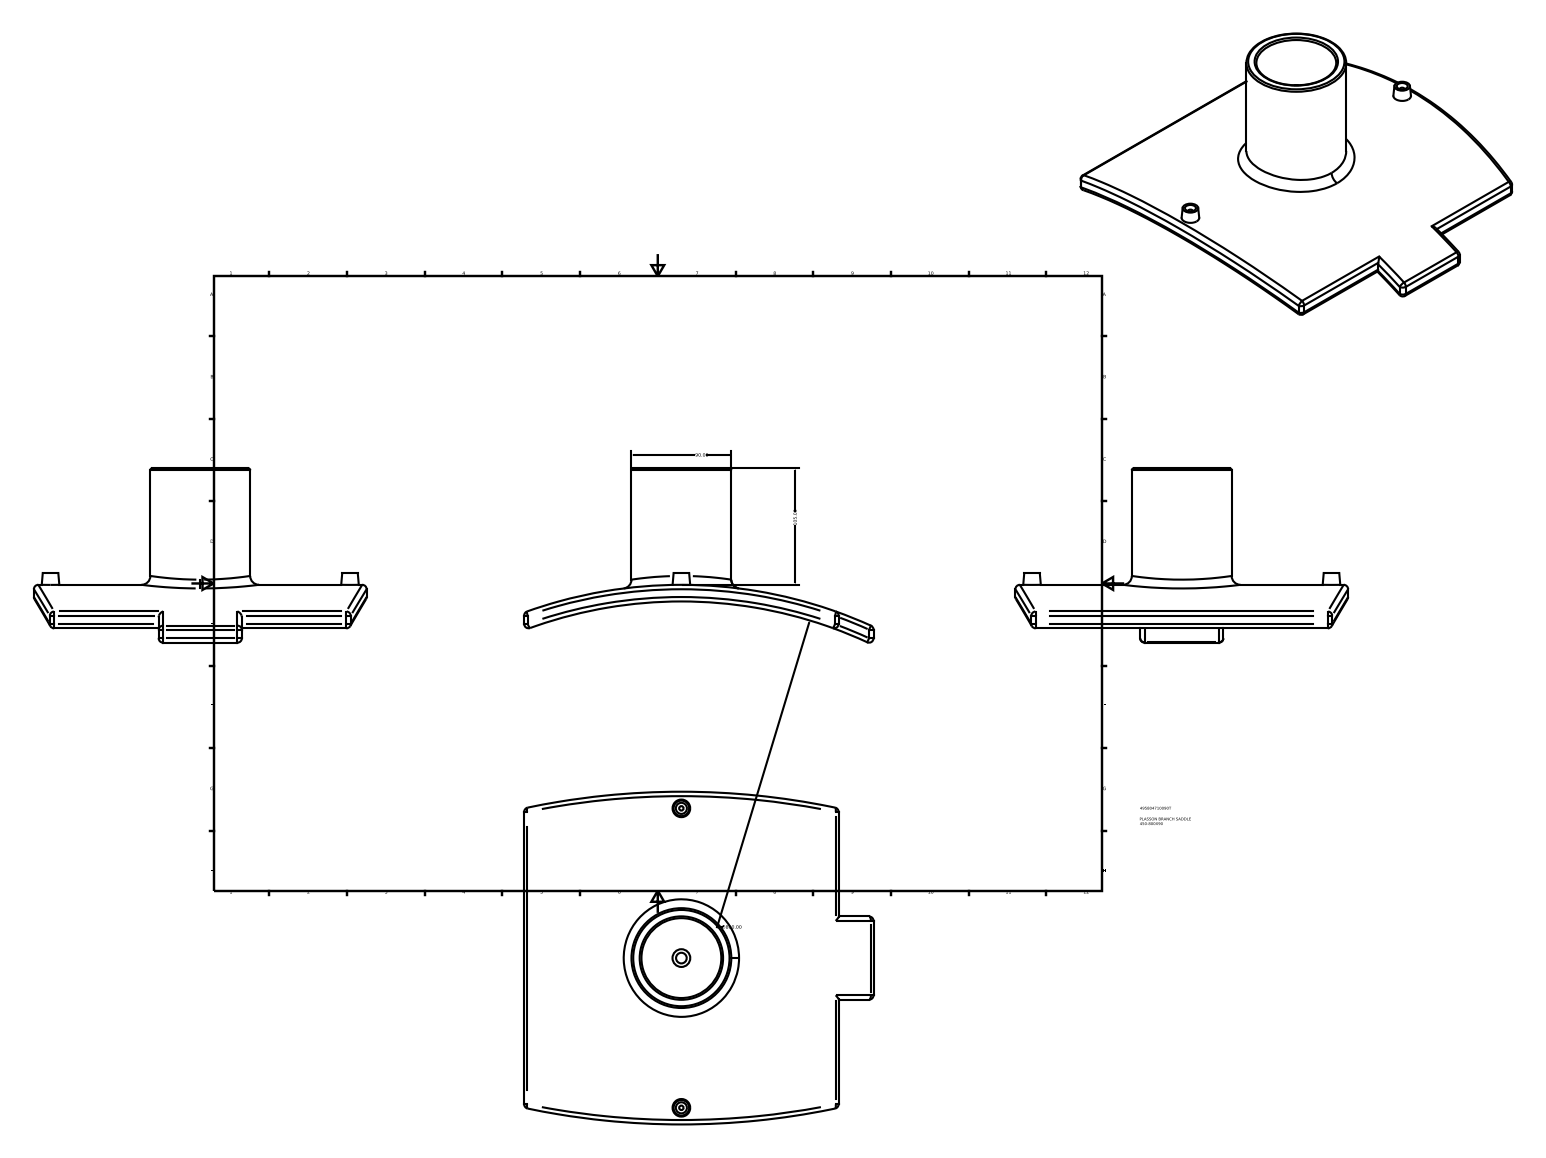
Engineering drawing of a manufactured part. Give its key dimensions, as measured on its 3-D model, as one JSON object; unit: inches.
{"part_name": "495804710090T", "step_written_by": "Autodesk Inventor 2015 (AUTOMOTIVE_DESIGN)", "units": "inches", "bodies": {"solids": 1, "faces": 66, "planar": 14, "cylindrical": 27, "other": 25}, "overall_size": [12.402, 11.811, 6.187], "volume_in3": 94.22, "surface_area_in2": 383.9, "round_holes": [[0.394, 2], [0.378, 1], [2.835, 1]], "round_bosses_or_shafts": [[0.157, 2], [3.543, 1], [0.63, 1]], "partial_cylinders_radius": [[0.157, 12], [26.664, 2], [15.748, 1], [16.339, 1]], "face_to_face_distances": [11.161, 1.24, 12.402, 2.953, 3.717, 0.551, 4.268, 3.028, 2.476, 0.433], "hole_center_spacings": [5.315, 10.63]}
